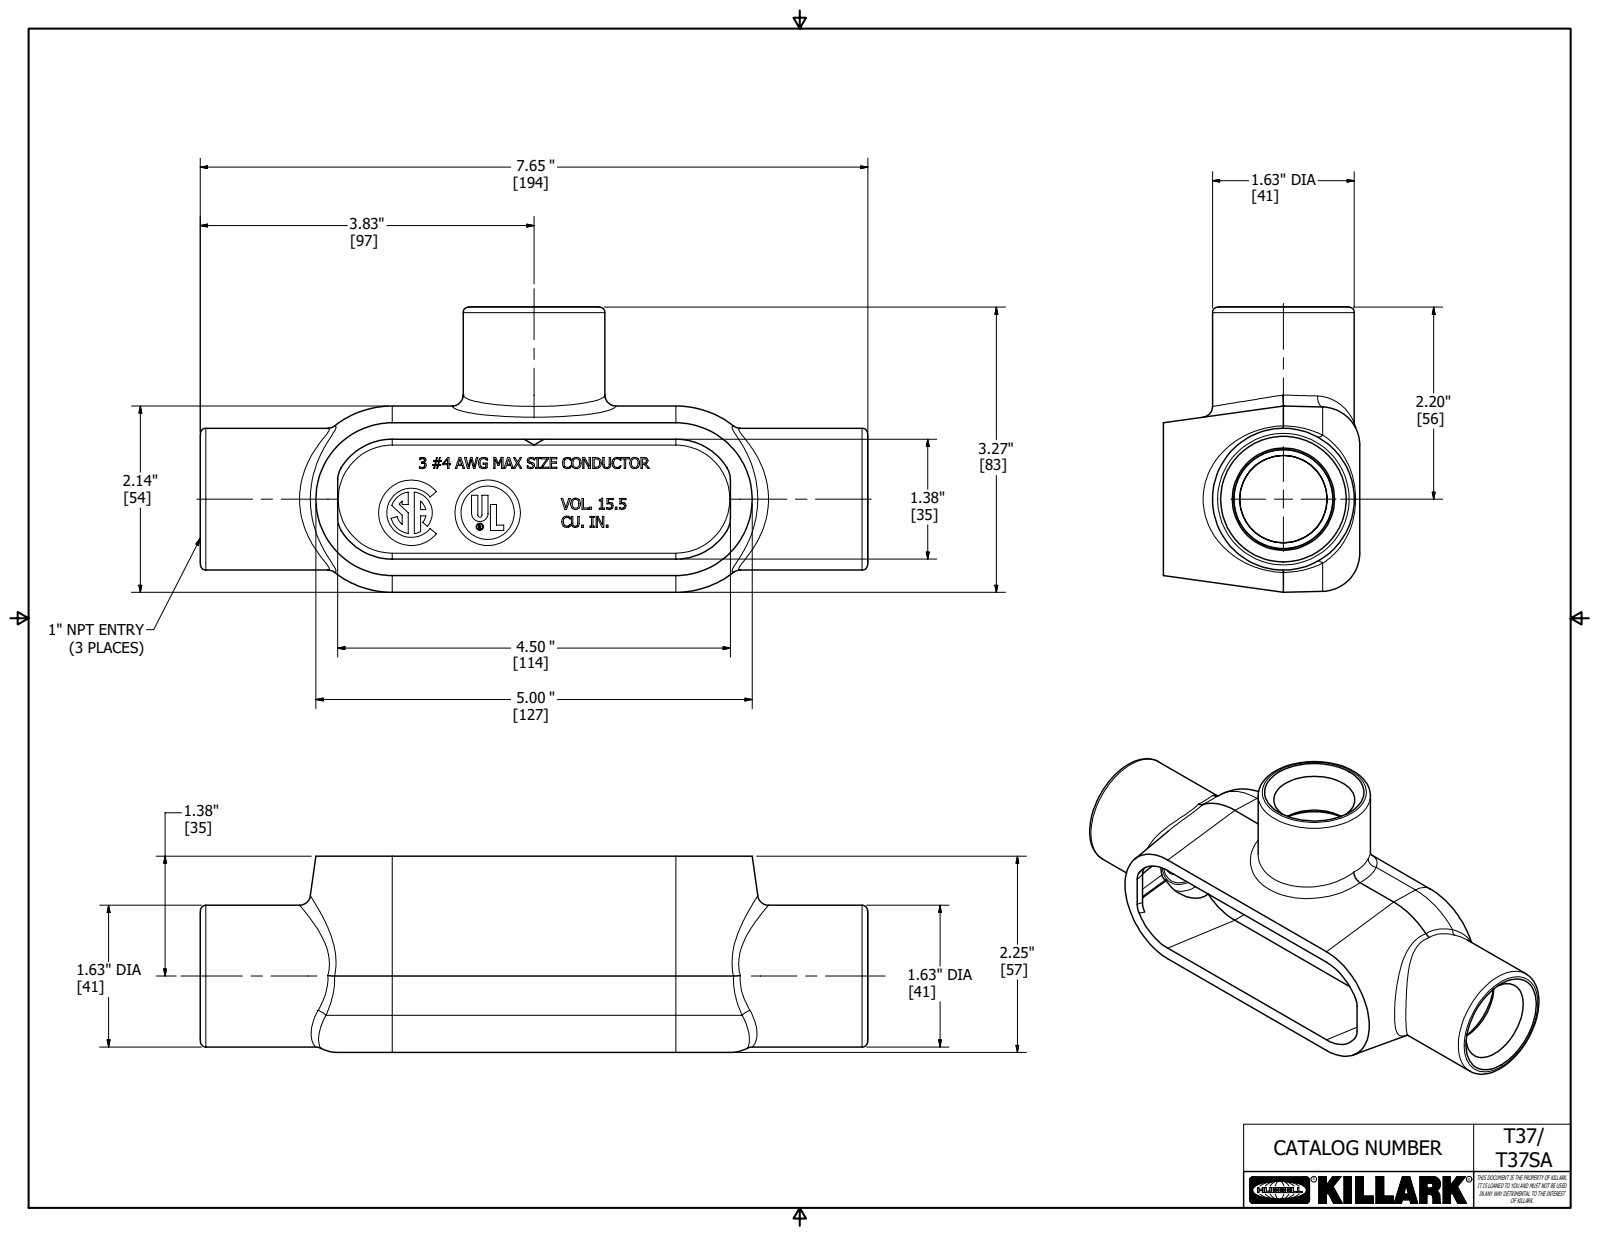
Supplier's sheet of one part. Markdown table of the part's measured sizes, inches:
| quantity | value |
| --- | --- |
| part name | 17673-2 |
| STEP written by | Autodesk Inventor 2018 (AUTOMOTIVE_DESIGN) |
| units | inches |
| bodies | 1 solid, 851 faces (518 planar, 41 cylindrical, 292 other) |
| overall size | 7.65 × 3.271 × 2.25 |
| volume | 9.131 in³ |
| surface area | 100.8 in² |
| round holes (diameter × count) | 1.321 × 2, 0.07 × 1, 0.611 × 1, 1.375 × 1 |
| round bosses / shafts (diameter × count) | 1.625 × 2, 0.75 × 1, 0.083 × 1 |
| partial cylindrical surfaces (radius × count) | 0.062 × 4, 0.125 × 4, 0.25 × 2, 0.437 × 2, 0.008 × 1, 0.013 × 1, 0.024 × 1, 0.094 × 1 |
| main face-to-face distances | 0.185, 0.187, 2.25, 2.063, 0.219, 0.031, 2.031, 0.031, 0.156, 0.188 |
| hole center spacings | 0.183 |
